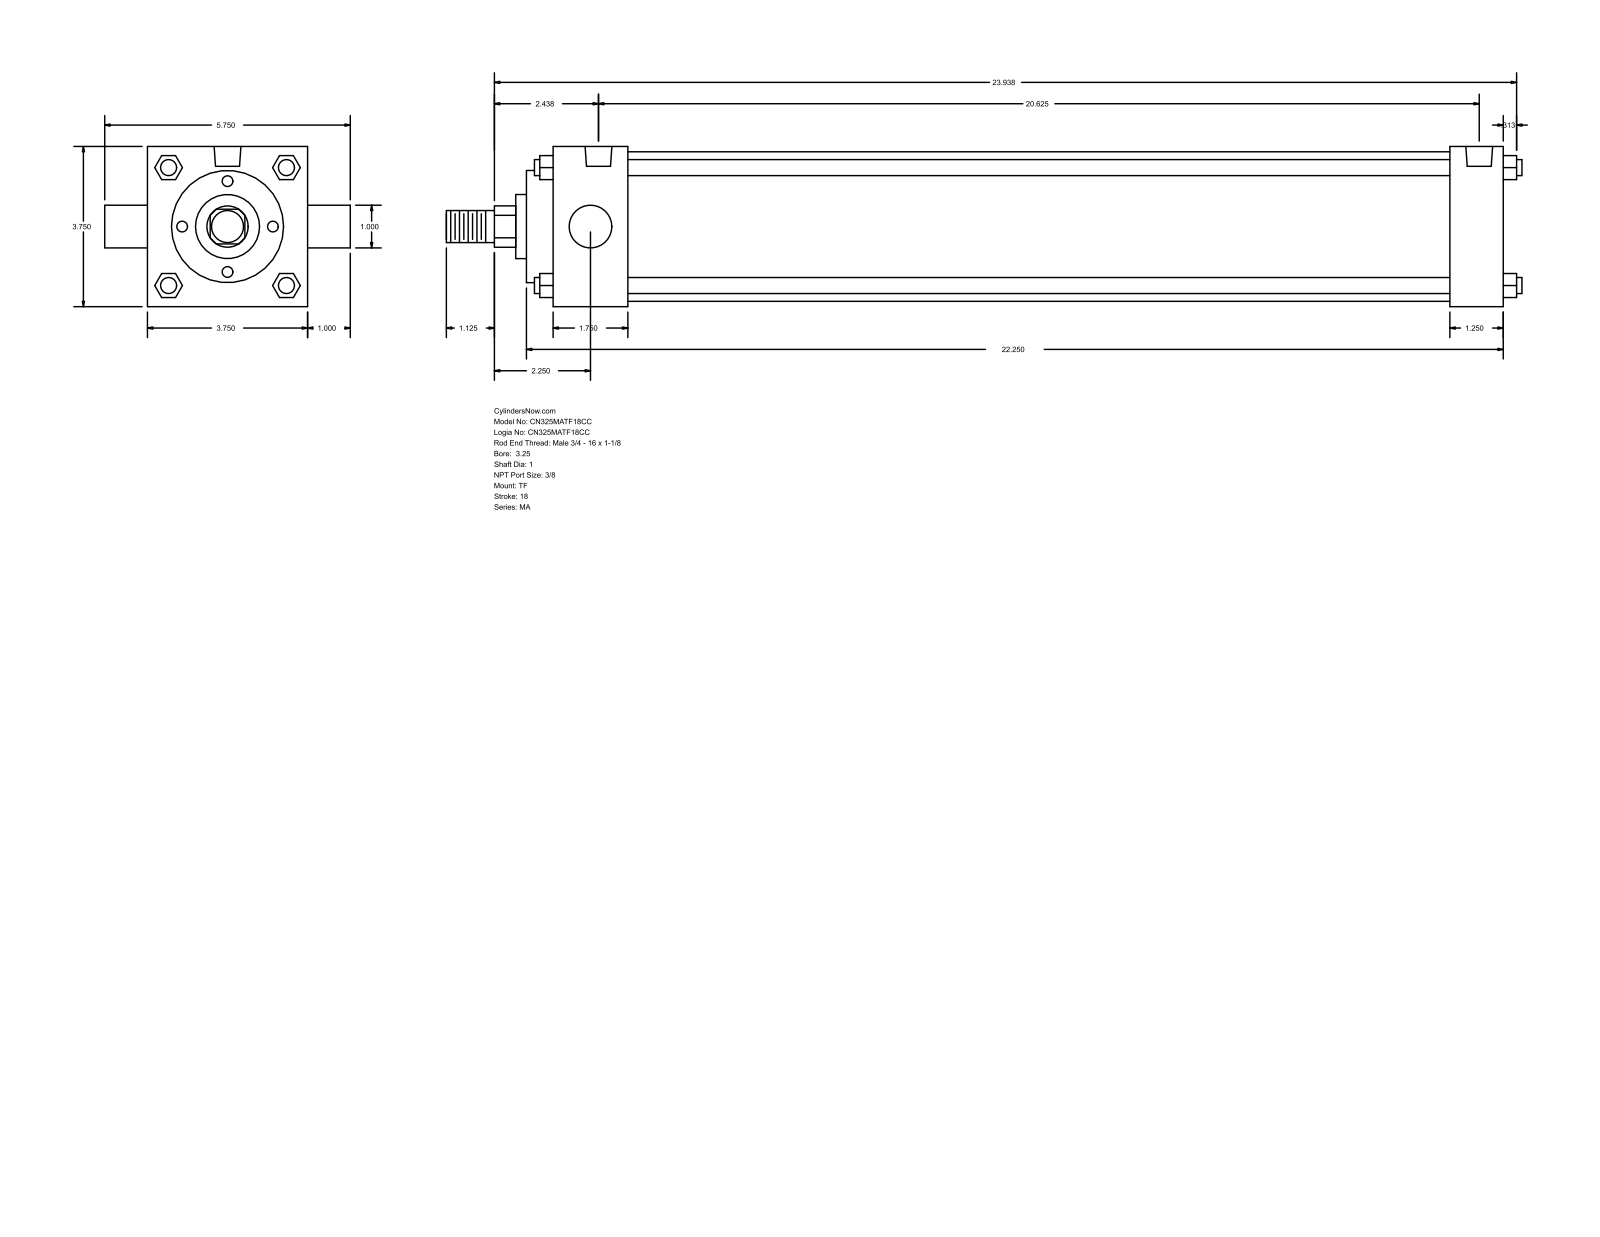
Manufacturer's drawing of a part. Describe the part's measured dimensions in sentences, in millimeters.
The part is named "MA_TF__0325_1". Its 3-D file was written by "GSSL Pune (CONFIG_CONTROL_DESIGN)". It is 0 solids with 122 faces: 93 planar, 29 cylindrical and 0 other. Overall it measures 639.76 by 146.05 by 95.25 millimeters. Round holes: 3 of diameter 11.11, 2 of diameter 15.93. Round bosses or shafts: 4 of diameter 9.53, 2 of diameter 25.4, 1 of diameter 88.9, 1 of diameter 66.67, 1 of diameter 38.1, 1 of diameter 19.05. Partial cylindrical surfaces (rounded edges, fillets, slot ends): 1 of radius 12.29. The main face-to-face distances are 95.24, 565.16, 44.46, 533.41, 488.95, 520.7, 31.75, 15.87, 60.33, 549.28. The hole center spacings are 4.76, 4.77, 514.35, 519.11, 519.12, 523.88.
